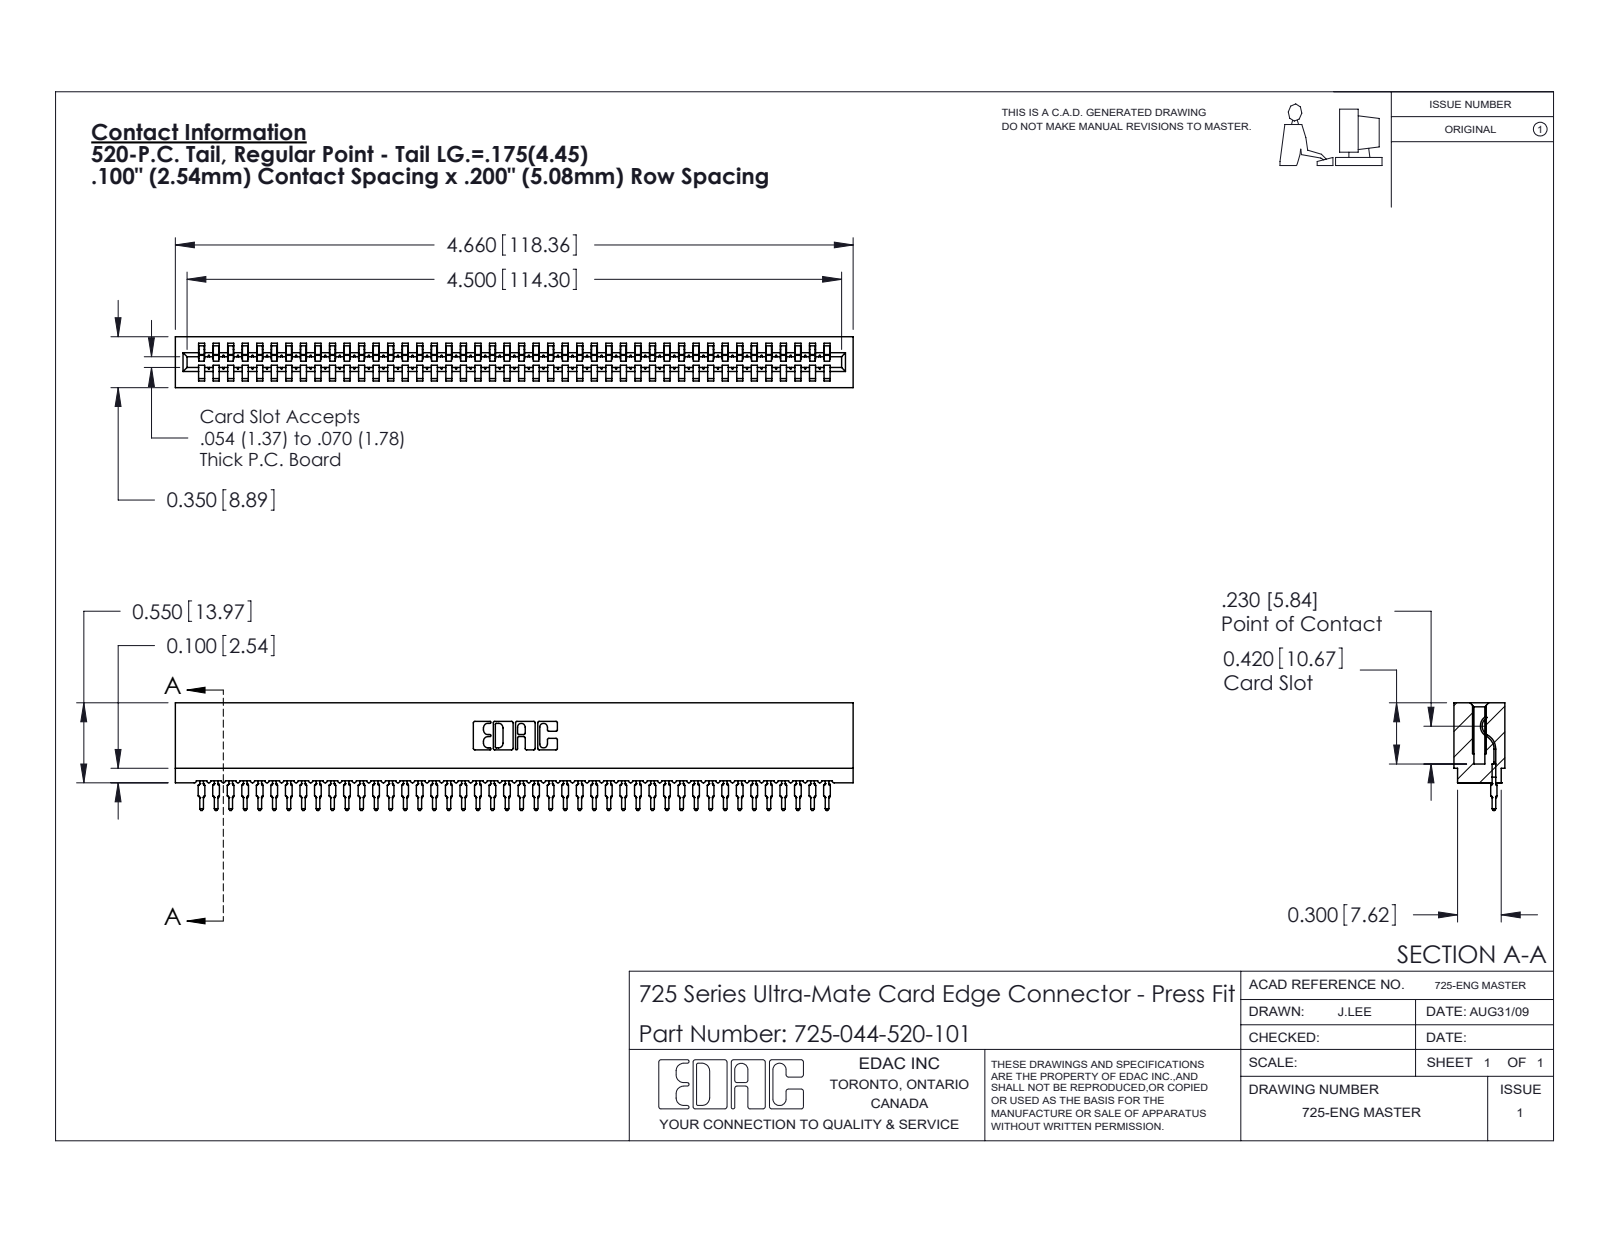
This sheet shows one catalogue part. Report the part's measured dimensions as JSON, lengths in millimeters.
{"part_name": "725-044-520-101; 745-292-001_520; 725 Part_Insulator Option - 01", "step_written_by": "SolidWorks 2020 (CONFIG_CONTROL_DESIGN)", "units": "millimeters", "bodies": {"solids": 45, "faces": 5023, "planar": 3003, "cylindrical": 876, "other": 1144}, "overall_size": [118.4, 18.8, 8.9], "volume_mm3": 8910, "surface_area_mm2": 16940, "partial_cylinders_radius": [[0.4, 88], [0.5, 88], [0.3, 22], [0.2, 6], [0.8, 6], [0.1, 4], [0.3, 4], [0.7, 3]], "face_to_face_distances": [8.9, 5.1, 5.4, 3.5, 2.5, 1.1, 7.7, 2.4, 4.2, 7.6]}
